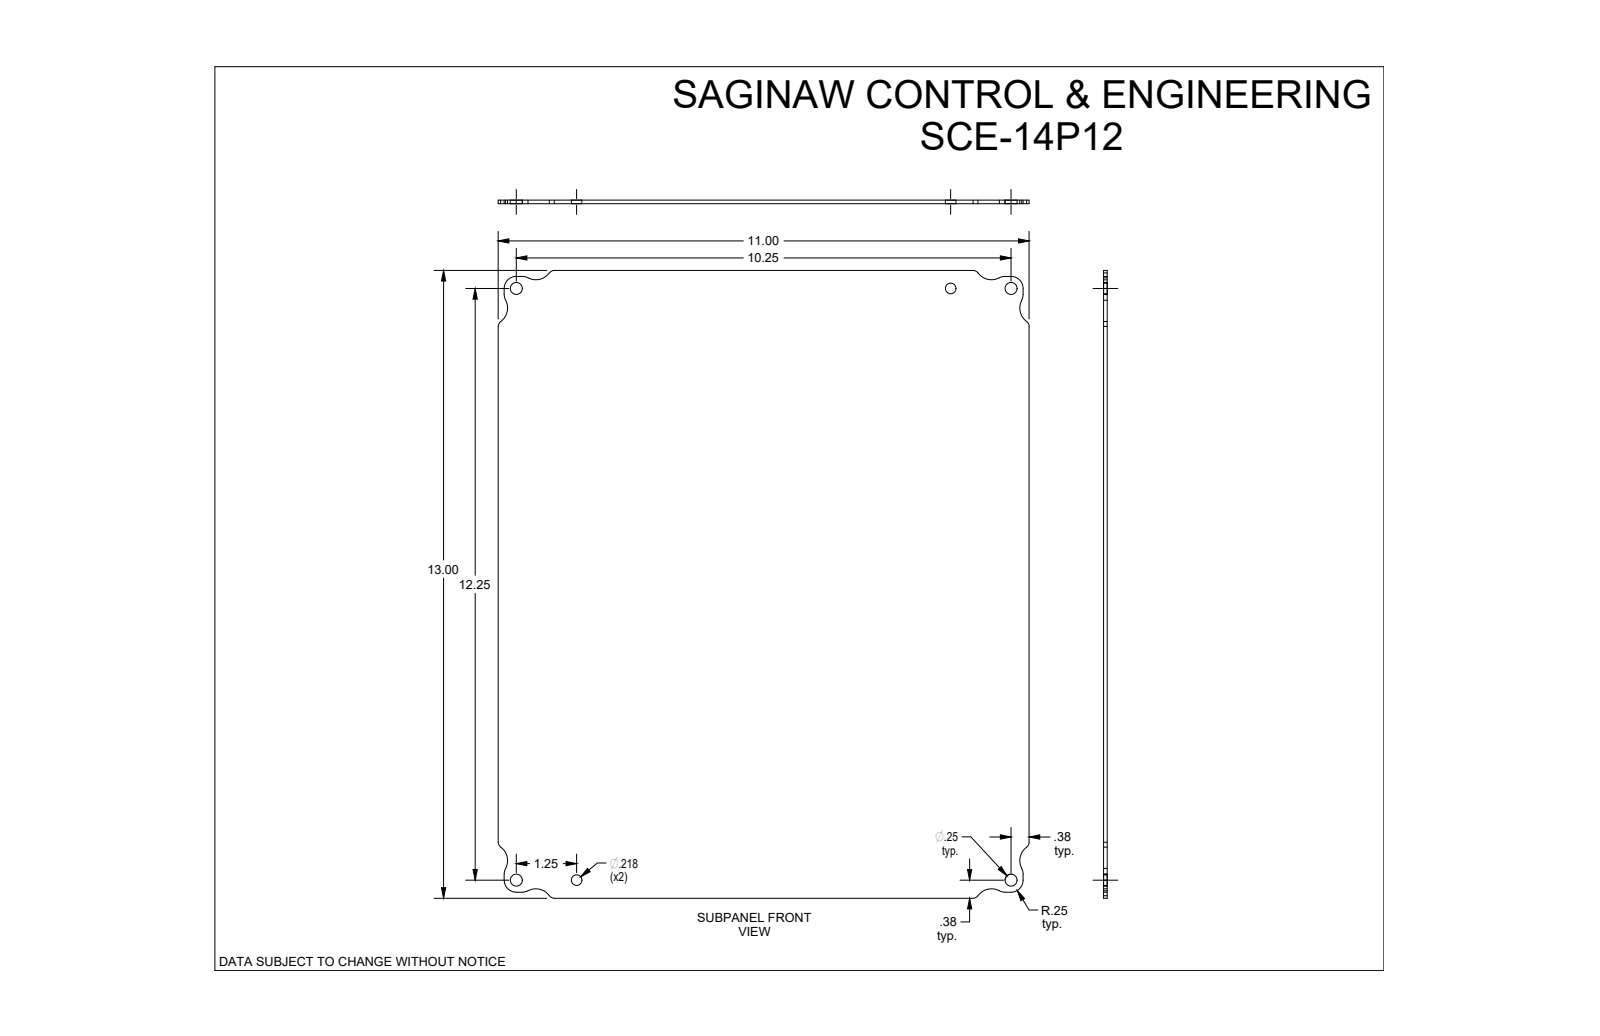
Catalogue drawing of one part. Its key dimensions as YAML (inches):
part_name: "SCE-14P12"
step_written_by: "SolidWorks 2019 (CONFIG_CONTROL_DESIGN)"
units: inches
bodies: {solids: 1, faces: 48, planar: 14, cylindrical: 34, other: 0}
overall_size: [13, 11, 0.075]
volume: 10.61
surface_area: 286.9
round_holes:
  - {diameter: 0.25, count: 4}
  - {diameter: 0.218, count: 2}
partial_cylinders:
  - {radius: 0.25, count: 12}
  - {radius: 0.125, count: 8}
  - {radius: 0.344, count: 8}
face_to_face_distances: [0.075, 11, 13, 0.124, 10.876, 0.125, 12.875, 10.752, 12.75]
hole_center_spacings: [1.25, 9, 10.25, 12.25, 12.313, 15.2, 15.972, 14.495]
